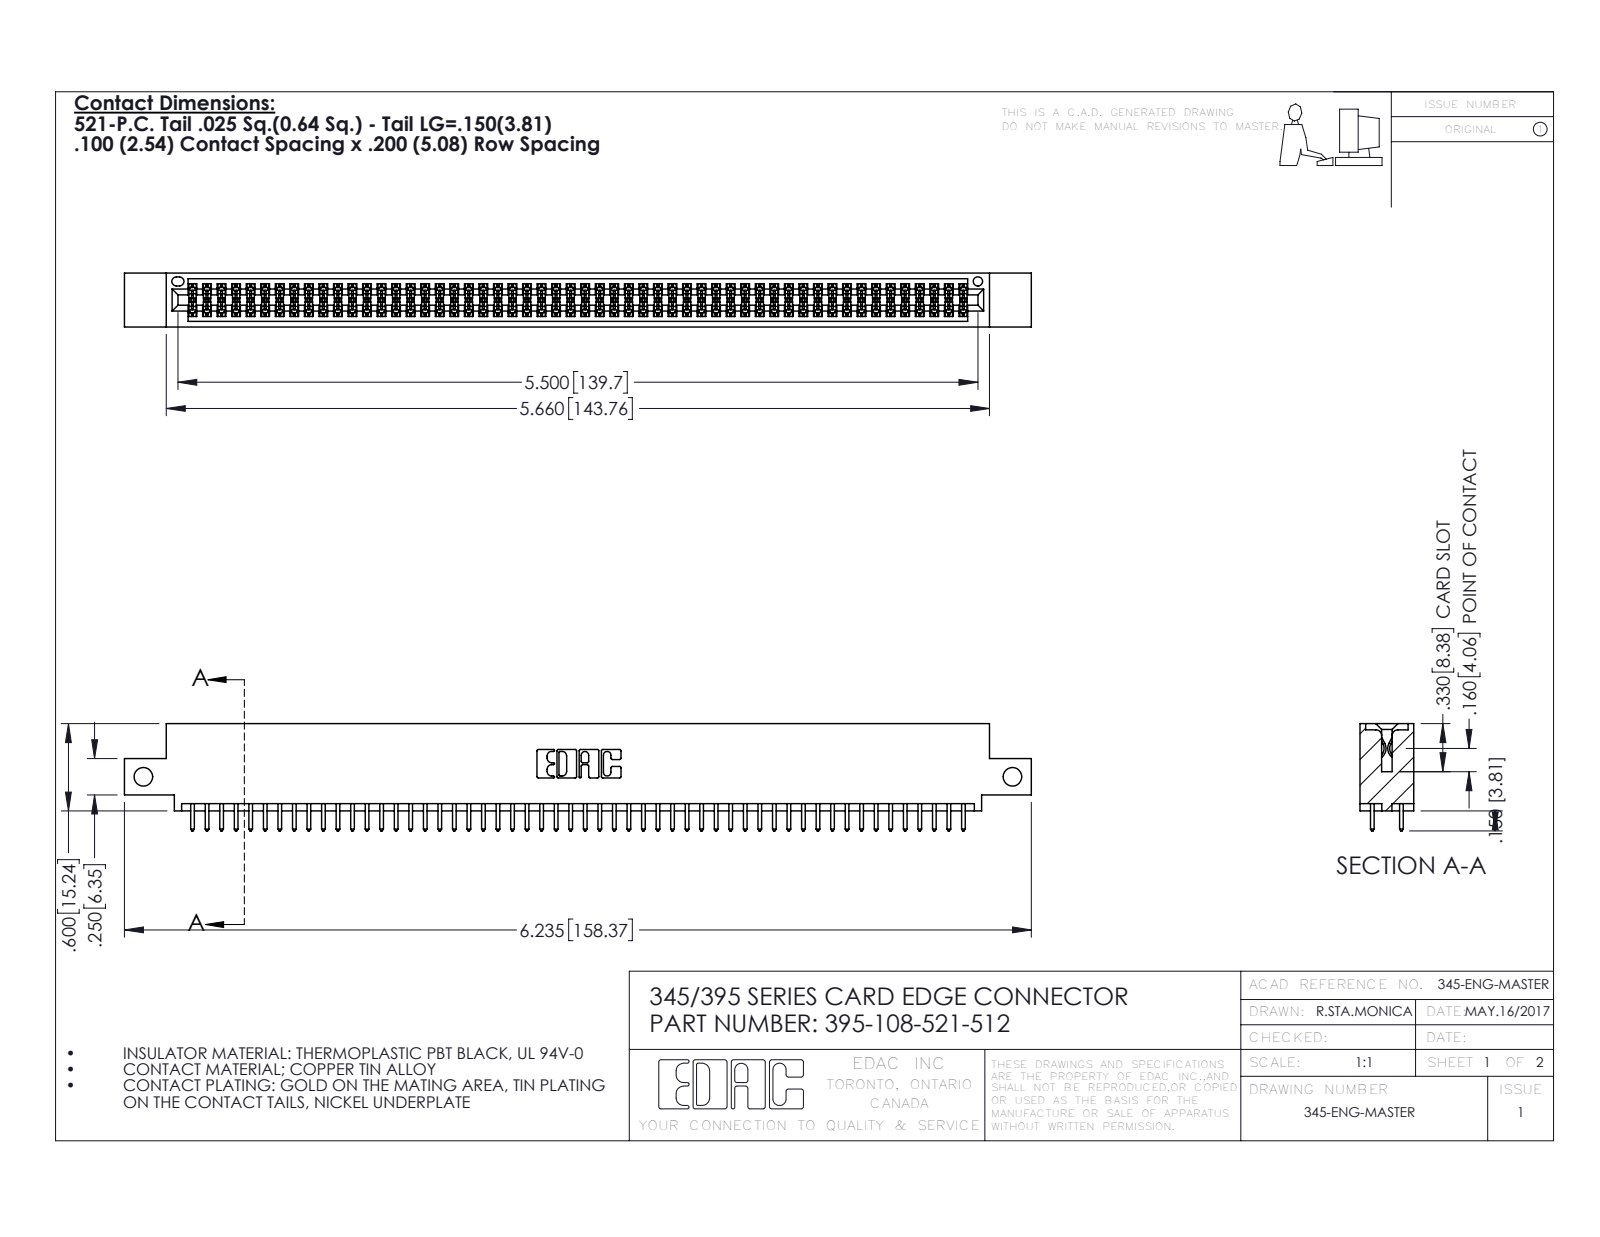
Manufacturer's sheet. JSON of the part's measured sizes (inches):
{"part_name": "345-292-001_345-293-121; 395-108-521-512; 345 Part_0.110 Offset - Side Mount", "step_written_by": "SolidWorks 2016 (CONFIG_CONTROL_DESIGN)", "units": "inches", "bodies": {"solids": 109, "faces": 5530, "planar": 3648, "cylindrical": 1882, "other": 0}, "overall_size": [6.235, 0.737, 0.37], "volume_in3": 0.933, "surface_area_in2": 34.88, "round_holes": [[0.128, 2], [0.064, 1]], "partial_cylinders_radius": [[0.006, 162], [0.01, 108], [0.01, 22], [0.007, 6], [0.031, 6], [0.026, 3], [0.014, 2], [0.019, 2]], "face_to_face_distances": [0.298, 0.072, 0.2, 0.098, 0.272, 0.025, 0.37, 0.225, 0.175, 0.149], "hole_center_spacings": [5.975]}
